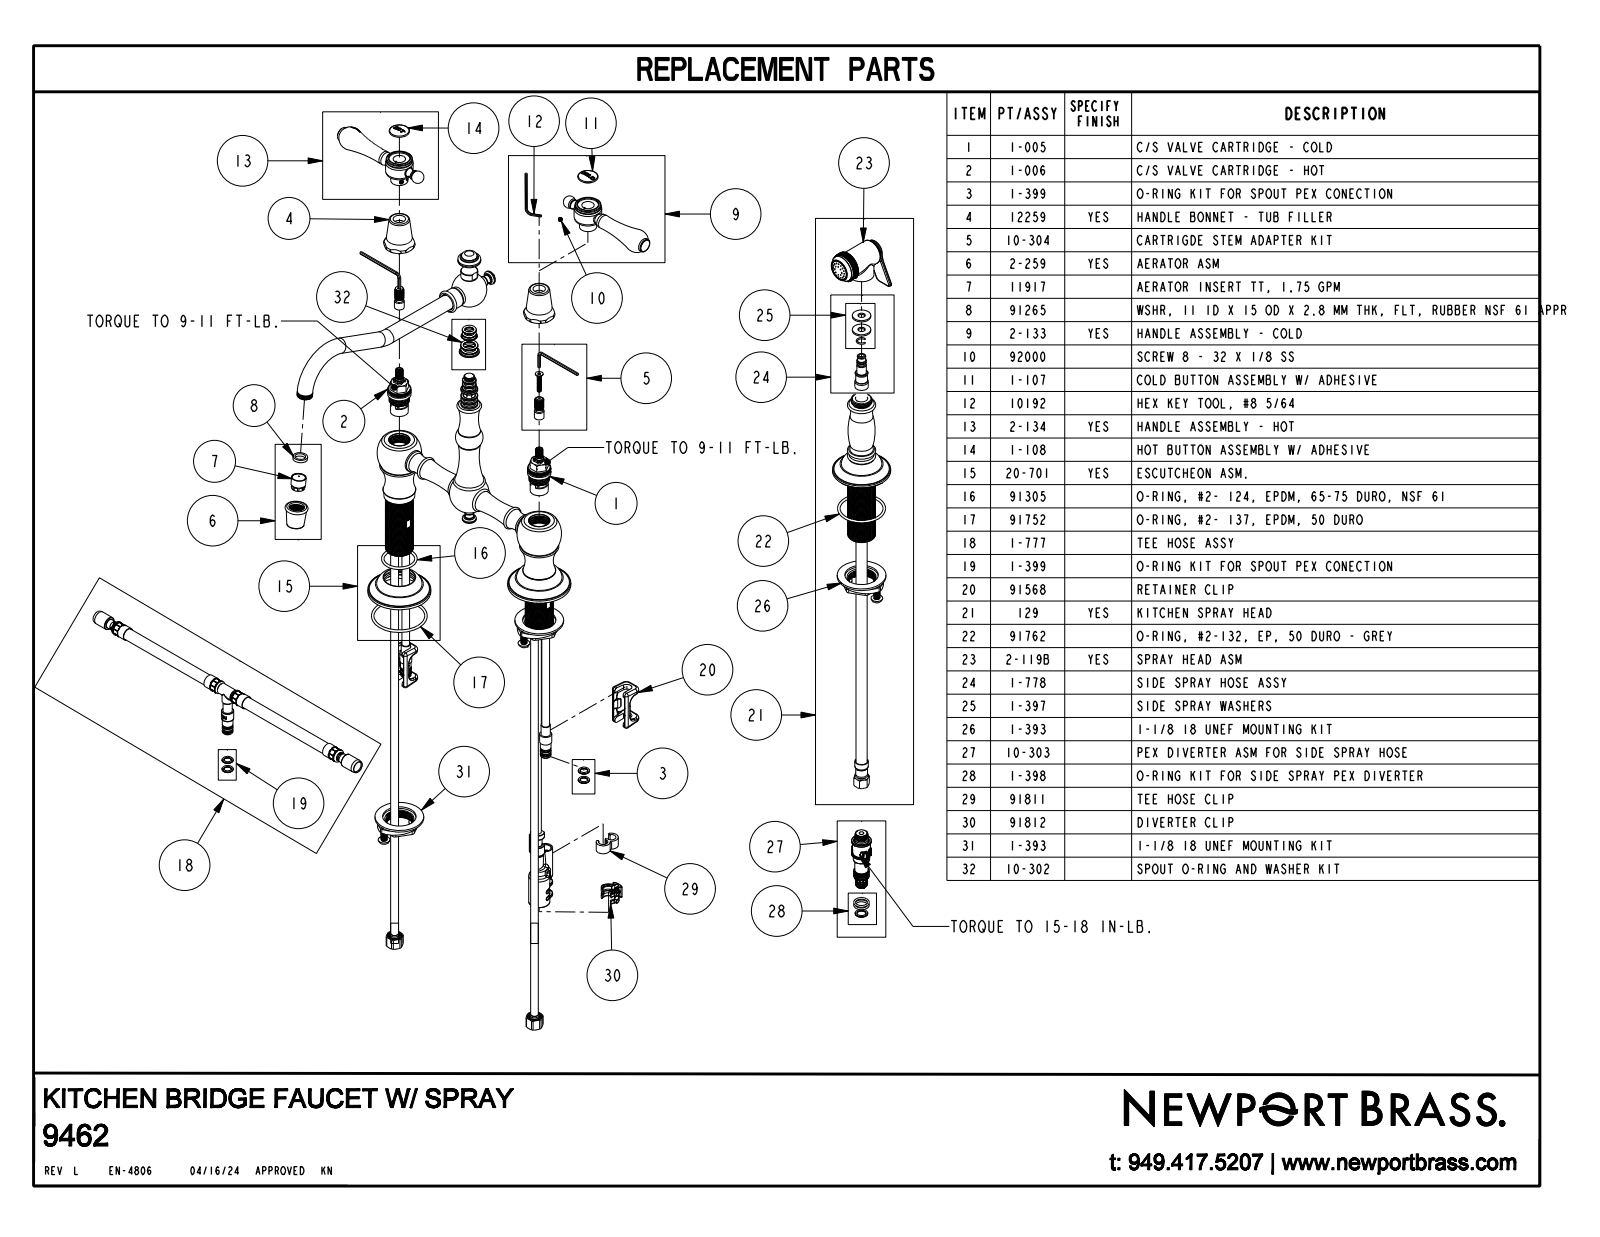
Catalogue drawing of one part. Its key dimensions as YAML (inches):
part_name: "9462"
step_written_by: "CREO PARAMETRIC BY PTC INC, 2018400 (AUTOMOTIVE_DESIGN)"
units: inches
bodies: {solids: 5, faces: 1038, planar: 401, cylindrical: 289, other: 348}
overall_size: [17.548, 11.248, 9.297]
volume: 34.29
surface_area: 182
round_holes:
  - {diameter: 0.855, count: 2}
  - {diameter: 0.06, count: 1}
  - {diameter: 0.231, count: 1}
  - {diameter: 0.564, count: 1}
  - {diameter: 0.689, count: 1}
  - {diameter: 0.812, count: 1}
  - {diameter: 0.968, count: 1}
round_bosses_or_shafts:
  - {diameter: 2.35, count: 3}
  - {diameter: 0.625, count: 3}
  - {diameter: 1.115, count: 2}
  - {diameter: 1.055, count: 2}
  - {diameter: 0.687, count: 2}
  - {diameter: 0.562, count: 2}
  - {diameter: 0.405, count: 2}
  - {diameter: 0.357, count: 2}
partial_cylinders:
  - {radius: 0.04, count: 10}
  - {radius: 0.006, count: 7}
  - {radius: 0.024, count: 7}
  - {radius: 0.03, count: 5}
  - {radius: 0.07, count: 5}
  - {radius: 0.06, count: 4}
  - {radius: 0.048, count: 3}
  - {radius: 0.018, count: 2}
face_to_face_distances: [0.13, 4.52, 4.54, 0.02, 0.05, 6.957, 2.437, 2.417, 0.38, 4.14]
hole_center_spacings: [4, 8]
